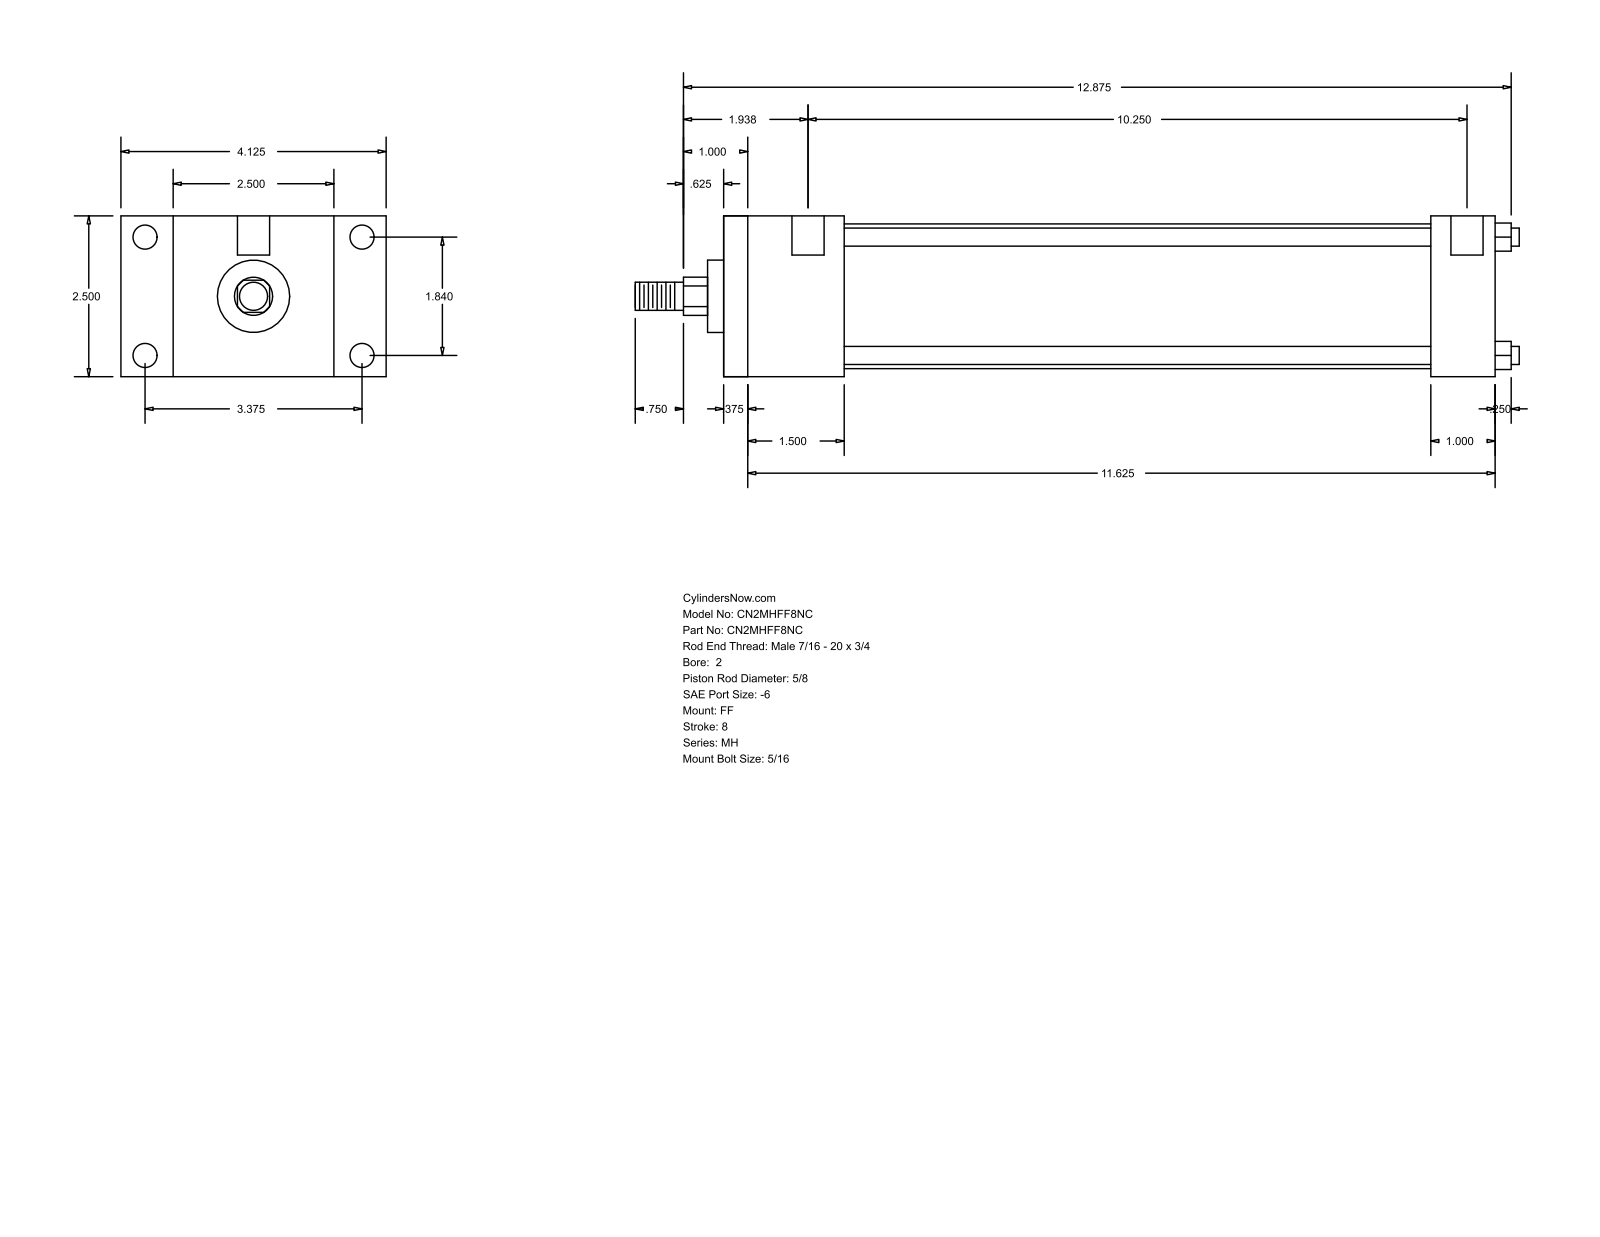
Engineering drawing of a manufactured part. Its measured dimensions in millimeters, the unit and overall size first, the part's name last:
Units: millimetres
Overall size (bounding box): 349.25 × 104.78 × 63.5
Round holes (diameter × count): ⌀5.56 ×4, ⌀9.53 ×4, ⌀12.7 ×2
Round bosses / shafts (diameter × count): ⌀7.14 ×4, ⌀57.15 ×1, ⌀28.57 ×1, ⌀15.88 ×1, ⌀11.11 ×1
Partial cylindrical surfaces — rounded edges, fillets, slot ends (radius × count): R7.54 ×1
Main face-to-face distances: 63.5, 304.8, 9.52, 295.28, 38.1, 47.62, 279.39, 269.87, 231.77, 257.18
Hole centre spacings: 46.74, 85.72, 97.63, 268.29, 3.18, 4.76, 260.35, 263.53
Bodies: 0 solids, 92 faces (64 planar, 28 cylindrical, 0 other)
Part name (STEP PRODUCT): MH_FF__0200_0.625
STEP written by: GSSL Pune (CONFIG_CONTROL_DESIGN)
